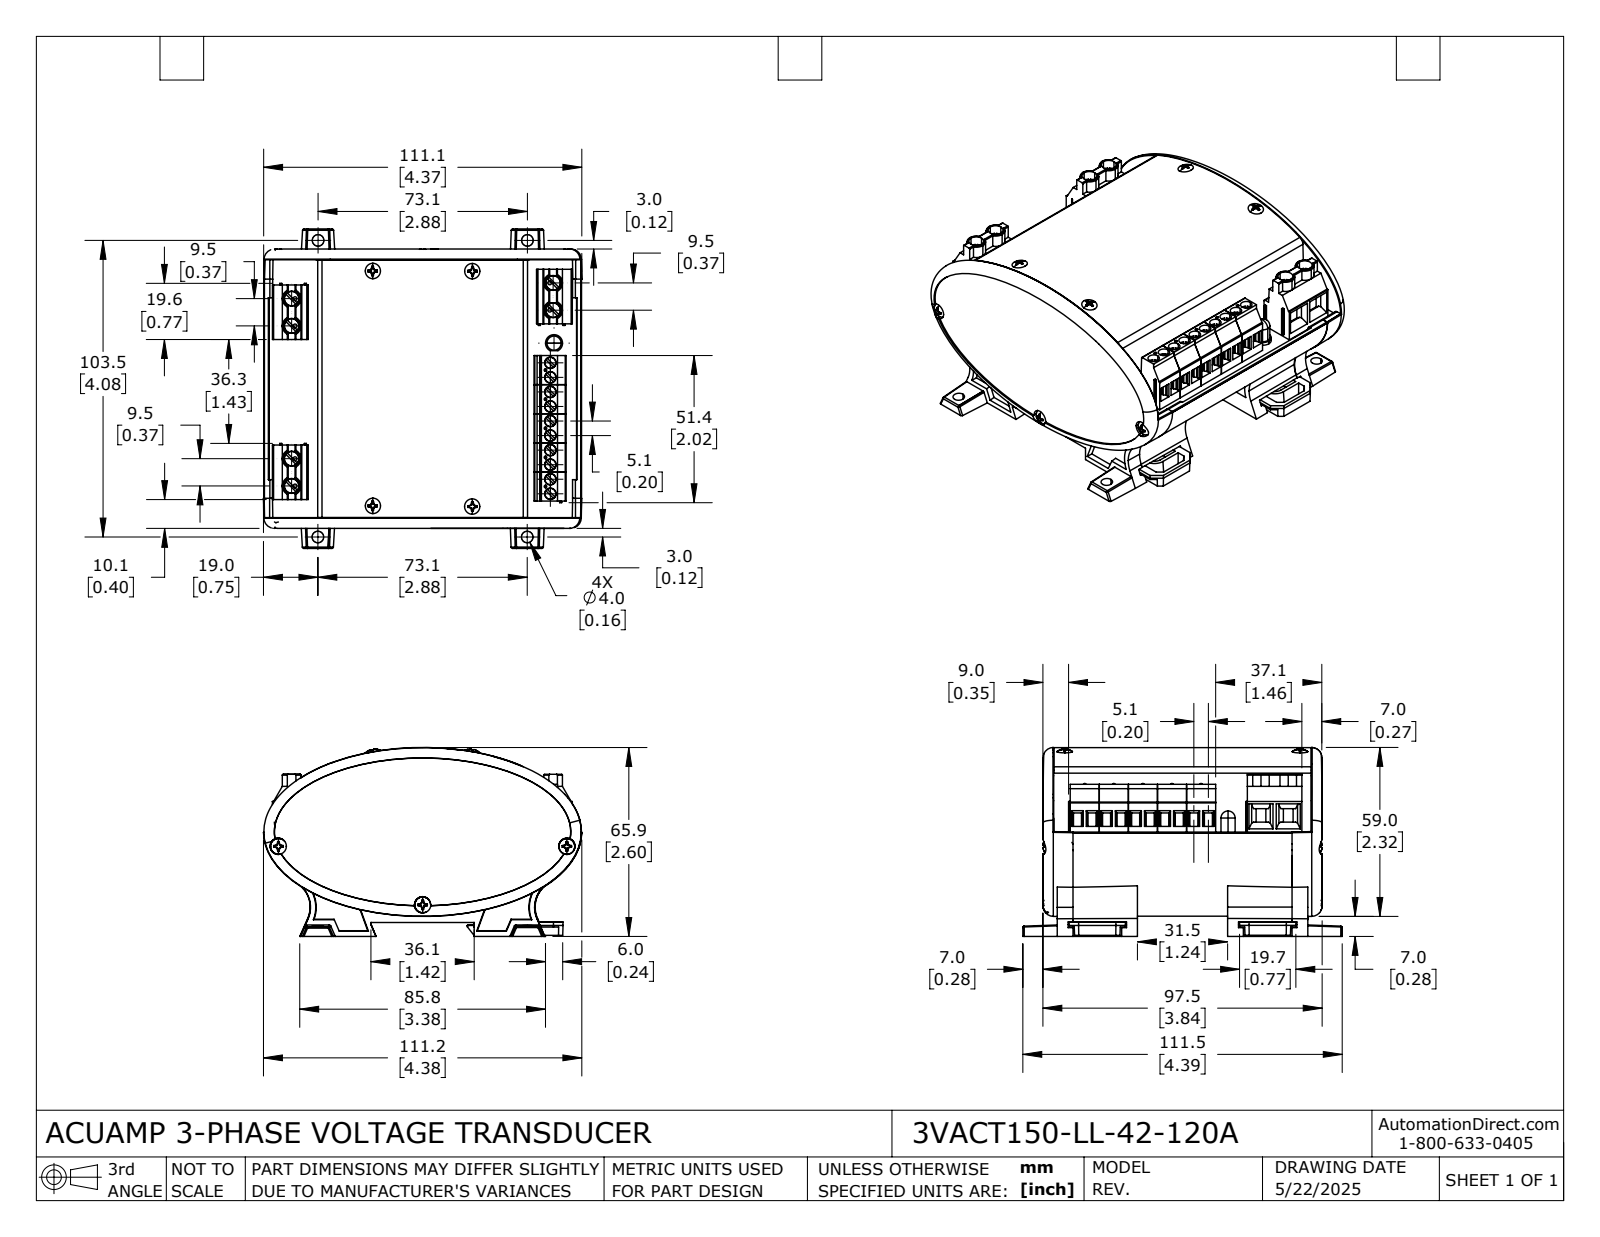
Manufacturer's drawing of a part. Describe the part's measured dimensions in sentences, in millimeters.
The part is named "3VACT150-LL-42-120A". Its 3-D file was written by "SolidWorks 2024 (AUTOMOTIVE_DESIGN)". It is 26 solids with 2967 faces: 1482 planar, 844 cylindrical and 641 other. Overall it measures 188.7 by 111.1 by 66 millimeters. Its volume is 192 700 cubic millimeters and its surface area 183 700 square millimeters. Round holes: 12 of diameter 1.3, 10 of diameter 4, 6 of diameter 2, 6 of diameter 5.2, 4 of diameter 3.2, 3 of diameter 2.8, 3 of diameter 7.1. Round bosses or shafts: 16 of diameter 1.3, 10 of diameter 3.8, 10 of diameter 2.8, 10 of diameter 1.7, 6 of diameter 5, 4 of diameter 0.5, 1 of diameter 5.9, 1 of diameter 4.9. Partial cylindrical surfaces (rounded edges, fillets, slot ends): 38 of radius 0.2, 20 of radius 1, 17 of radius 0.5, 12 of radius 0.2, 8 of radius 0.3, 6 of radius 0.3, 6 of radius 3.3, 4 of radius 0.5. The main face-to-face distances are 1.6, 3.3, 170.4, 2.1, 173.7, 167.2, 10, 163.7, 6.8, 160.4. The hole center spacings are 5.1, 10.2, 15.2, 20.3, 25.4, 30.5, 5.1, 5.1.
